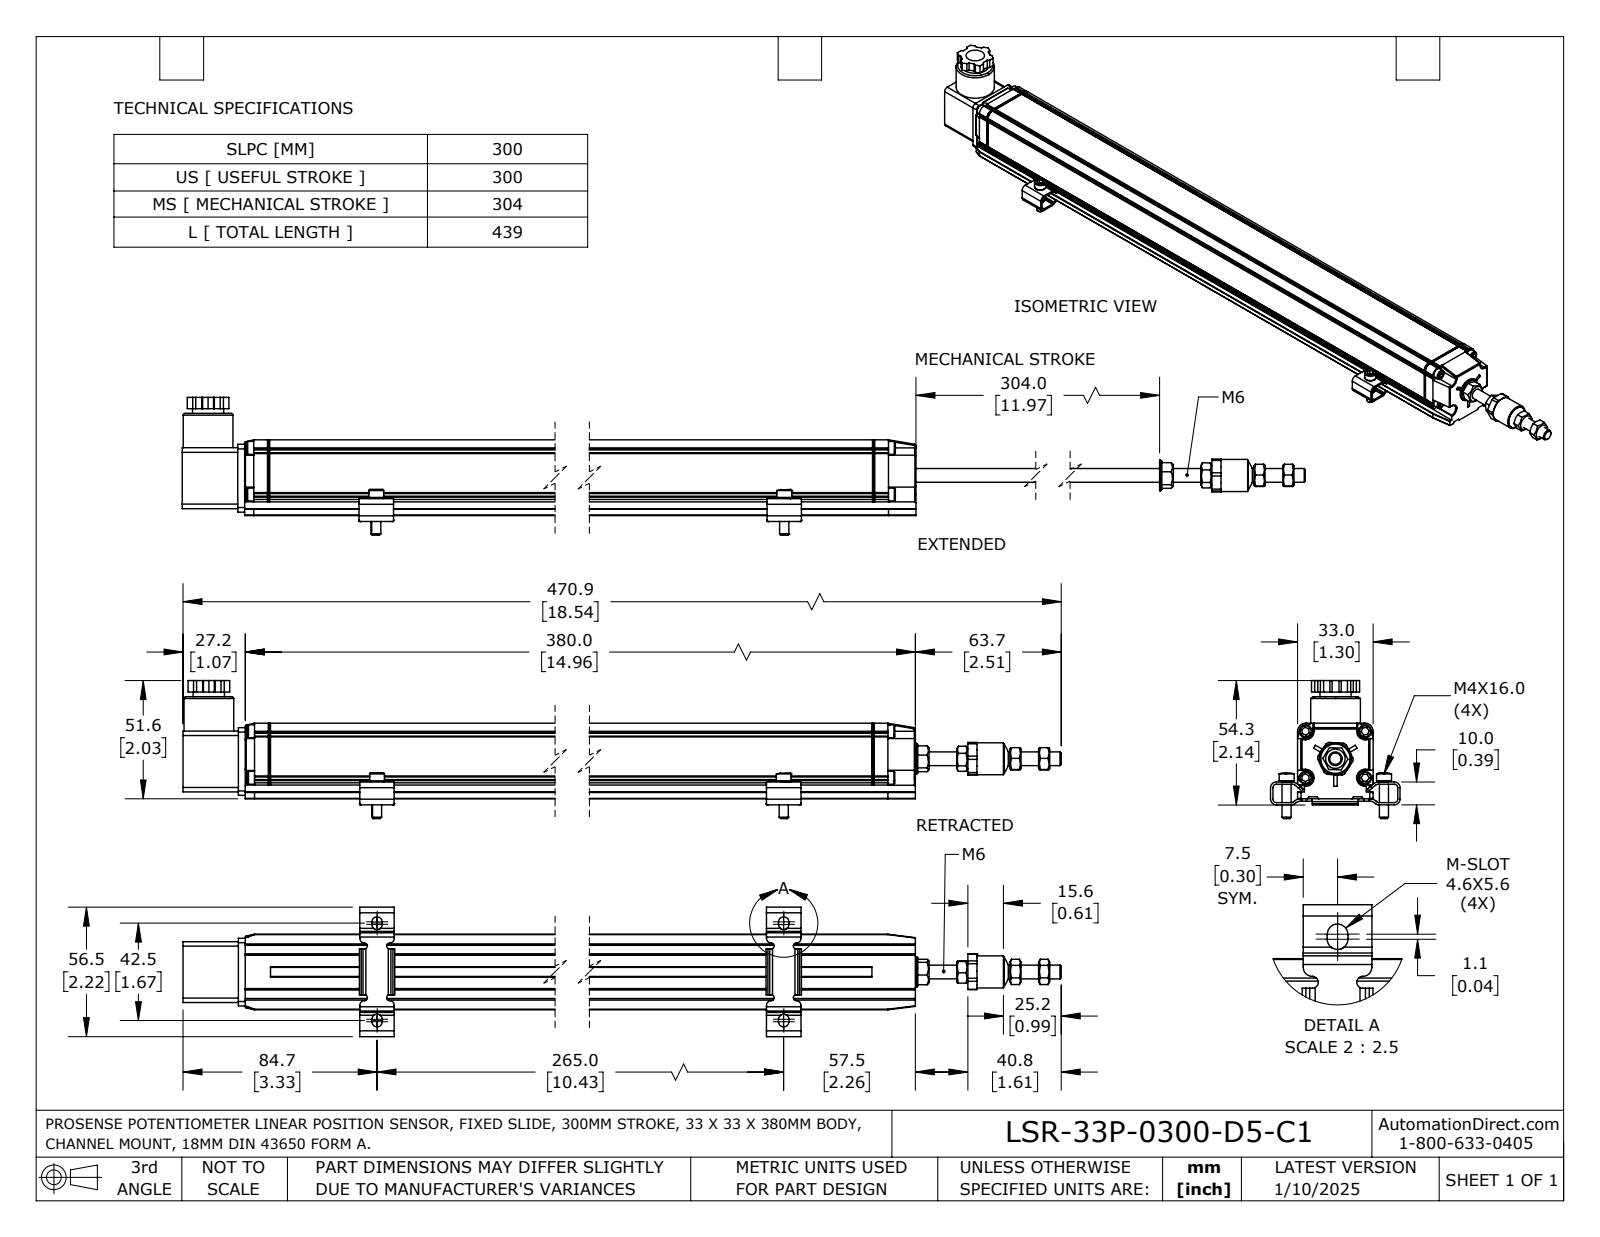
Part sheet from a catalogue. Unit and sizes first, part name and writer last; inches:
Units: inches
Overall size (bounding box): 18.537 × 2.37 × 2.224
Round holes (diameter × count): ⌀0.106 ×4, ⌀0.13 ×4, ⌀0.169 ×1, ⌀0.205 ×1, ⌀0.209 ×1, ⌀0.232 ×1, ⌀0.276 ×1, ⌀0.285 ×1, ⌀0.394 ×1, ⌀0.413 ×1, ⌀0.573 ×1, ⌀0.602 ×1
Round bosses / shafts (diameter × count): ⌀0.157 ×5, ⌀0.118 ×5, ⌀0.256 ×4, ⌀0.22 ×4, ⌀0.854 ×1, ⌀0.551 ×1, ⌀0.535 ×1, ⌀0.528 ×1
Partial cylindrical surfaces — rounded edges, fillets, slot ends (radius × count): R0.079 ×28, R0.02 ×23, R0.008 ×16, R0.051 ×8, R0.059 ×8, R0.089 ×8, R0.118 ×8, R0.039 ×4
Main face-to-face distances: 1.299, 0.118, 0.22, 0.039, 1.181, 1.079, 0.079, 0.102, 0.142, 0.185
Hole centre spacings: 0.047, 0.583, 0.607, 0.696, 0.73, 0.799, 1.024, 1.299
Volume: 23.94 in³ · Surface area: 161.8 in²
Bodies: 14 solids, 995 faces (641 planar, 269 cylindrical, 85 other)
Part name (STEP PRODUCT): LSR-33P-0300-D5-C1
STEP written by: SolidWorks 2023 (AUTOMOTIVE_DESIGN)
